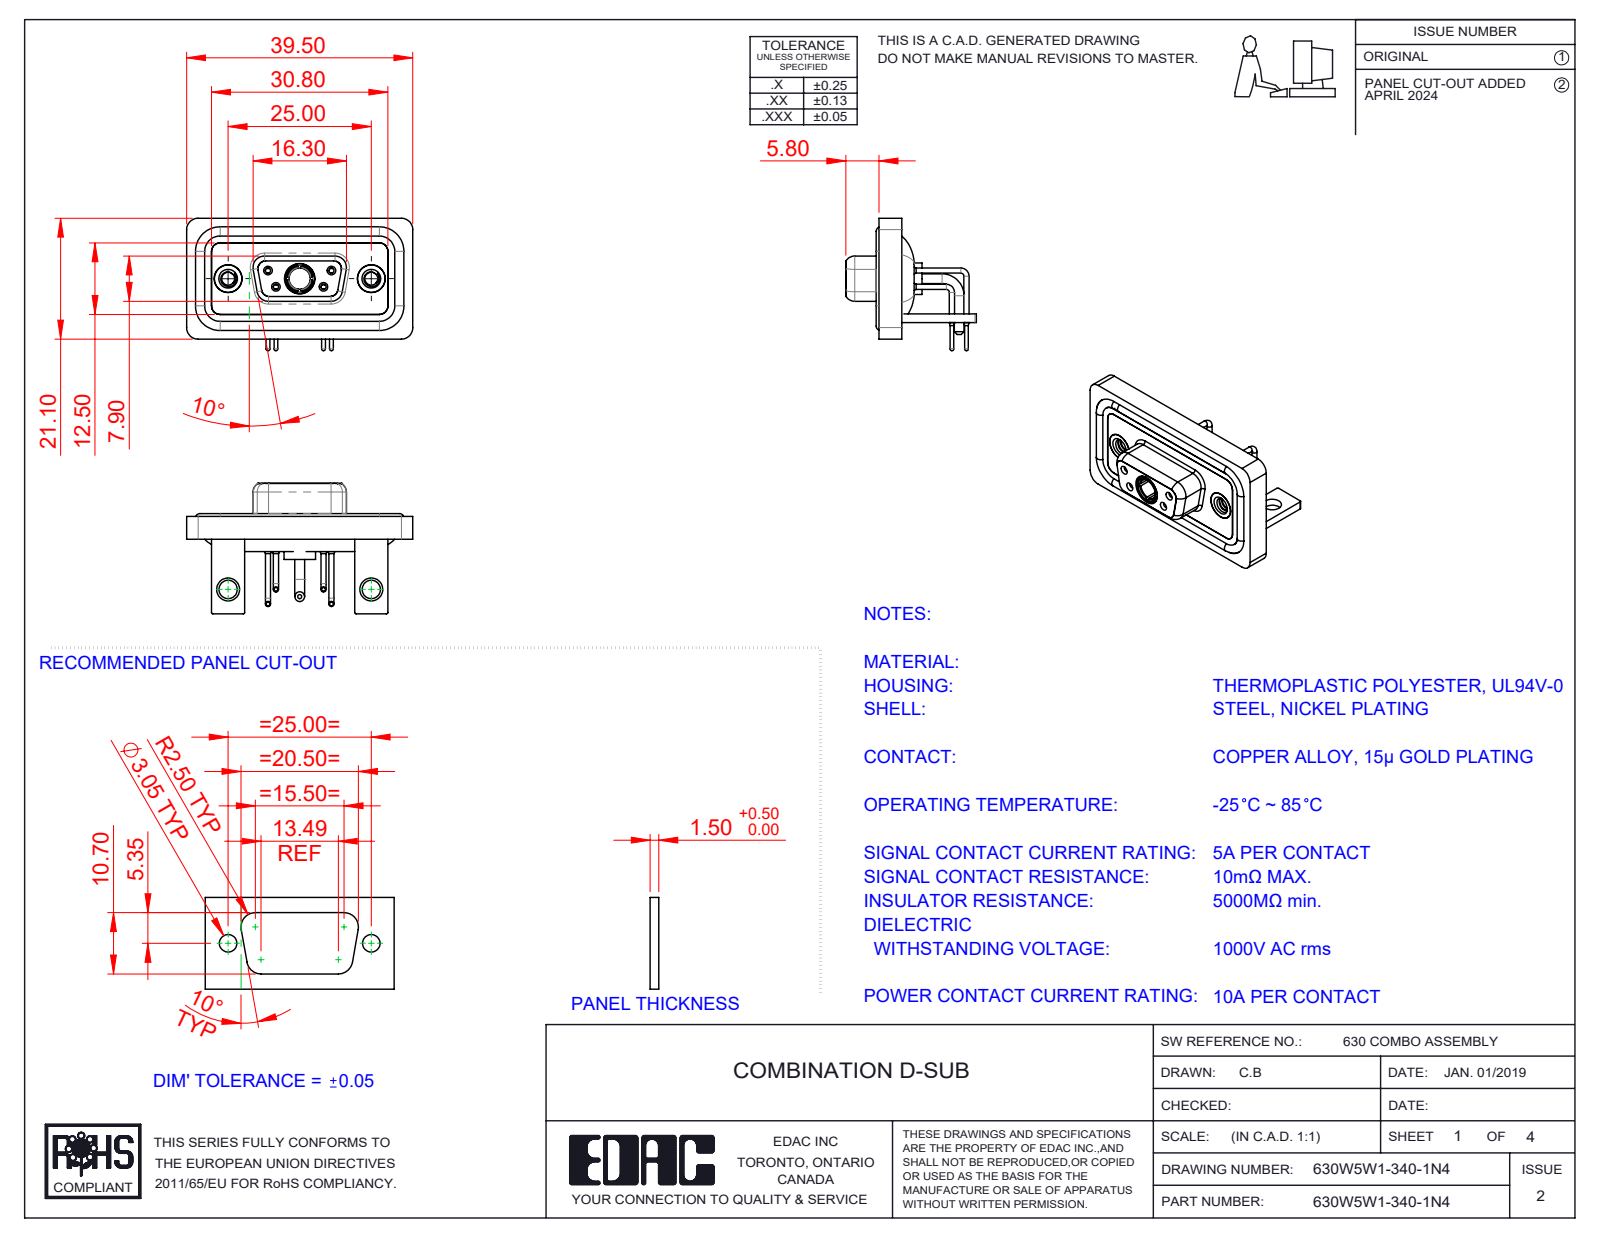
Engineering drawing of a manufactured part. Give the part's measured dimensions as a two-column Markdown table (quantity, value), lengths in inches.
| quantity | value |
| --- | --- |
| part name | 630Combo Contact Row 2_50 Contacts; 630Combo Shell Front_09 Contacts; 630Combo Waterproof Housing_09 Contacts; 630Combo Shell Rear_09 Contacts (+6 more) |
| STEP written by | SolidWorks 2023 (CONFIG_CONTROL_DESIGN) |
| units | inches |
| bodies | 15 solids, 724 faces (214 planar, 329 cylindrical, 181 other) |
| overall size | 1.555 × 0.91 × 0.898 |
| volume | 0.314 in³ |
| surface area | 13.22 in² |
| round holes (diameter × count) | 0.035 × 4, 0.043 × 4, 0.059 × 4, 0.079 × 4, 0.191 × 3, 0.063 × 2, 0.067 × 2, 0.089 × 2, 0.126 × 2, 0.157 × 2, 0.159 × 2, 0.197 × 2 |
| round bosses / shafts (diameter × count) | 0.063 × 6, 0.035 × 4, 0.026 × 4, 0.195 × 2, 0.189 × 2, 0.067 × 2, 0.217 × 1, 0.205 × 1 |
| partial cylindrical surfaces (radius × count) | 0.079 × 19, 0.059 × 18, 0.01 × 16, 0.053 × 8, 0.063 × 8, 0.02 × 5, 0.024 × 4, 0.026 × 4 |
| main face-to-face distances | 0.016, 0.114, 0.059, 0.071, 0.043, 0.146, 0.063, 0.031, 0.098, 0.122 |
| hole center spacings | 0.124, 0.225, 0.28, 0.492, 0.713, 0.984, 0.173, 0.173 |
